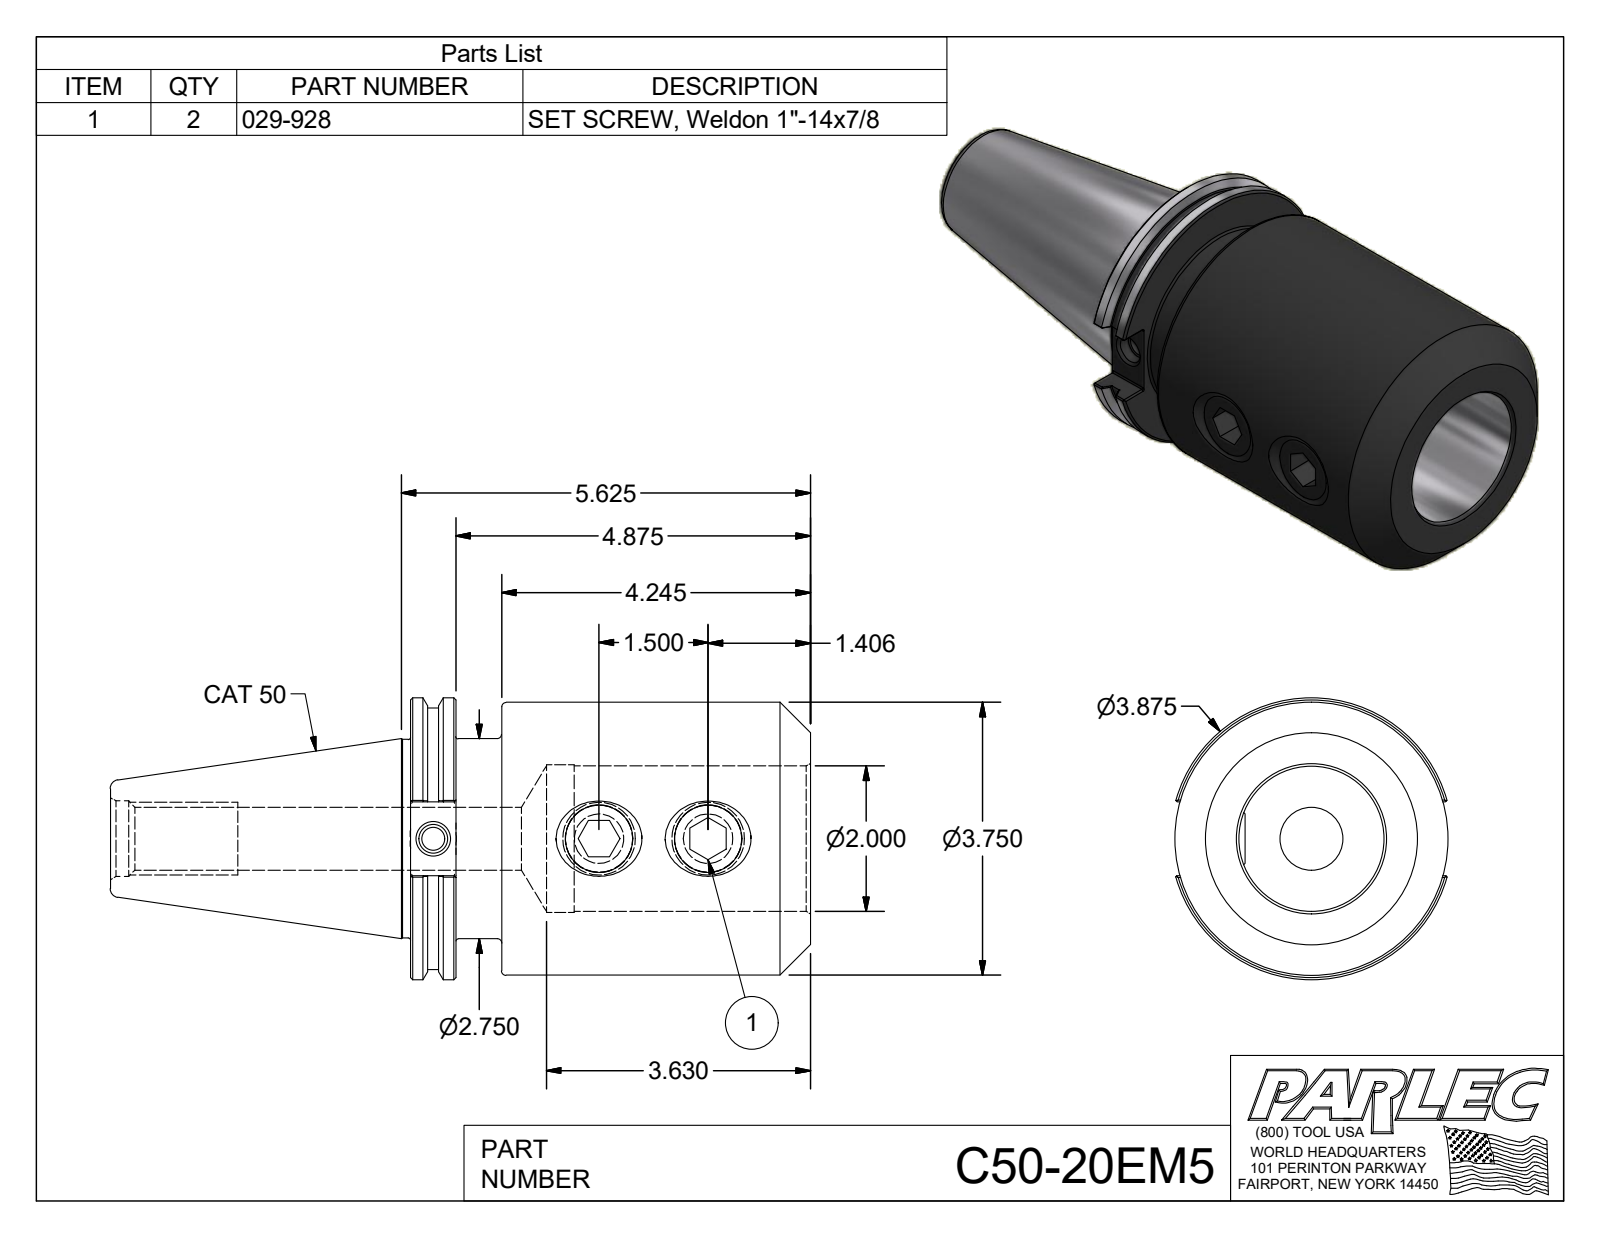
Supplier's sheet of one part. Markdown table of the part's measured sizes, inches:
| quantity | value |
| --- | --- |
| part name | C50-20EM5; C50-20EM5-1; 029-928 |
| STEP written by | Autodesk Inventor 2012 (AUTOMOTIVE_DESIGN) |
| units | inches |
| bodies | 3 solids, 119 faces (52 planar, 31 cylindrical, 36 other) |
| overall size | 9.625 × 3.875 × 3.75 |
| volume | 56.34 in³ |
| surface area | 167.4 in² |
| round holes (diameter × count) | 0.923 × 2, 0.315 × 1, 0.399 × 1, 0.865 × 1, 1.038 × 1, 2 × 1, 2.03 × 1 |
| round bosses / shafts (diameter × count) | 1 × 2, 3.875 × 1, 3.75 × 1, 3.594 × 1, 2.75 × 1, 2.73 × 1 |
| partial cylindrical surfaces (radius × count) | 0.02 × 12 |
| main face-to-face distances | 0.625, 1.255, 0.63, 5.5, 4.875, 4.245, 0.5, 0.875, 2.3, 3.175 |
| hole center spacings | 1.5, 2.279, 3.779 |
